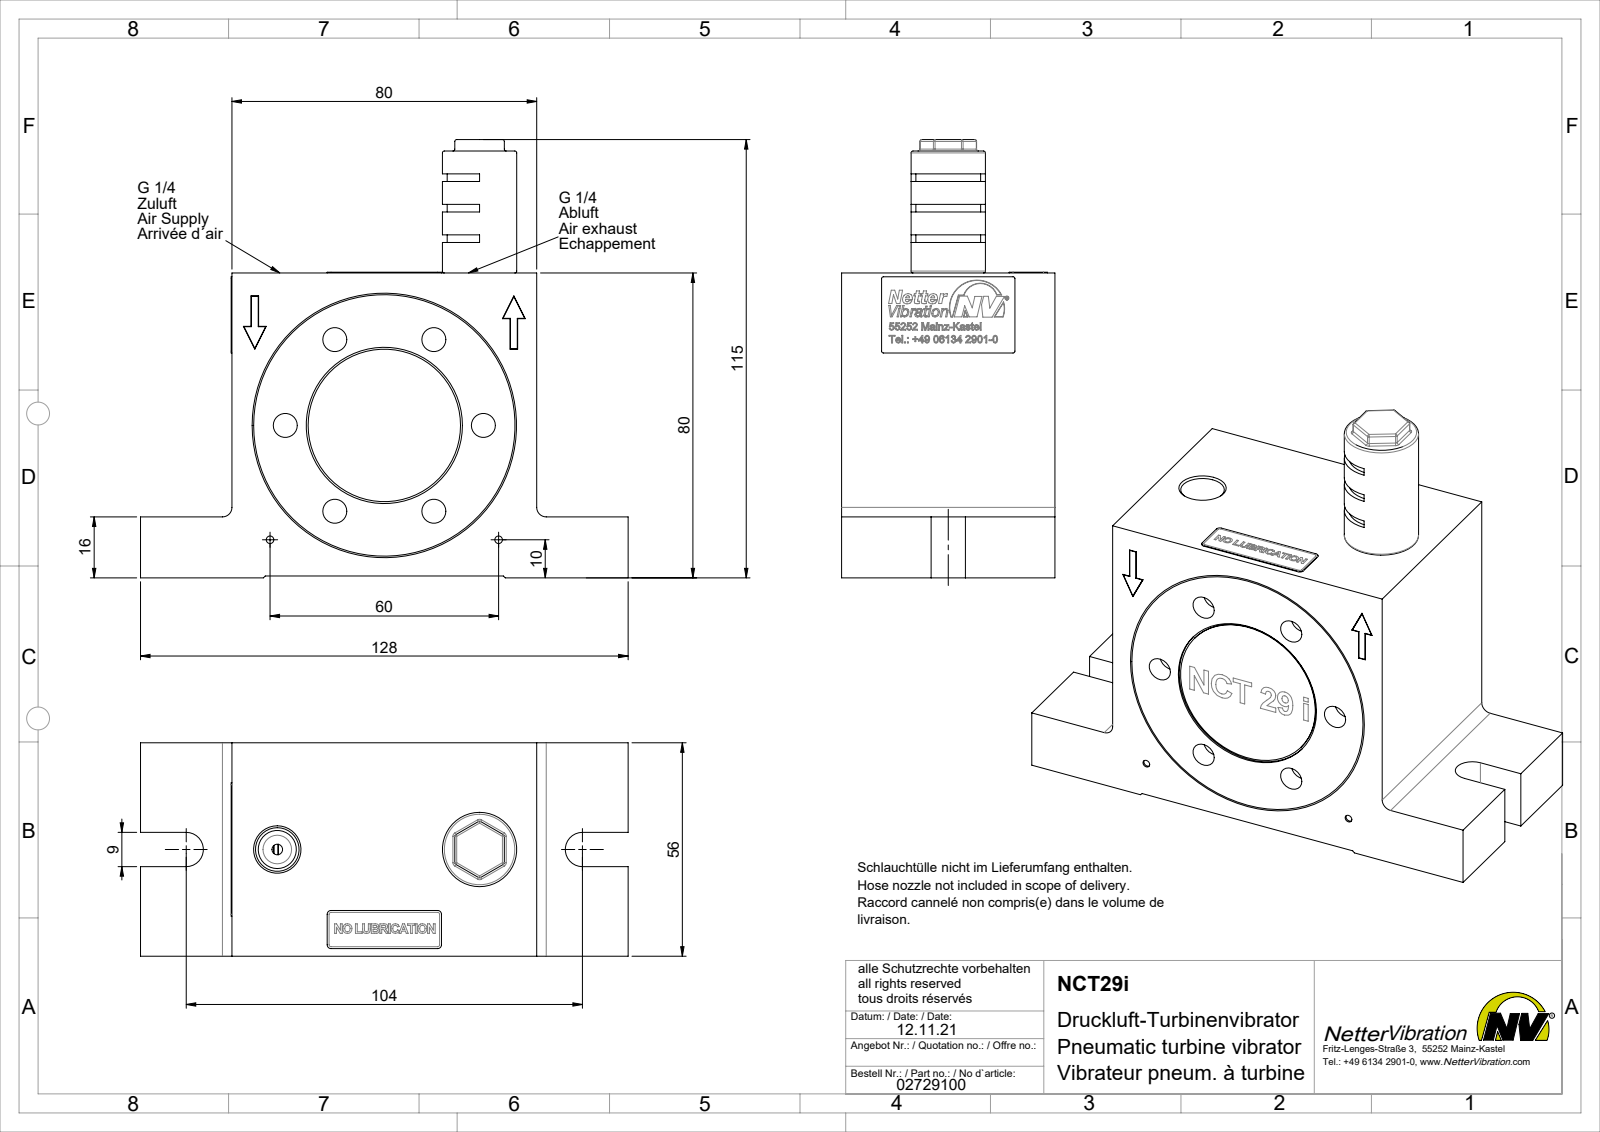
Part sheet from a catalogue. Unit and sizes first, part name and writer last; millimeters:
Units: millimetres
Overall size (bounding box): 128 × 115 × 56
Round holes (diameter × count): ⌀6.3 ×6, ⌀2 ×2, ⌀11.45 ×2, ⌀41 ×1, ⌀67.8 ×1
Round bosses / shafts (diameter × count): ⌀70 ×1, ⌀67.77 ×1, ⌀65.57 ×1, ⌀40 ×1, ⌀19.5 ×1, ⌀13.16 ×1
Partial cylindrical surfaces — rounded edges, fillets, slot ends (radius × count): R0.5 ×22, R1 ×4, R2.5 ×2, R4.5 ×2, R8.5 ×1
Main face-to-face distances: 80, 0.5, 56, 16, 8, 8.5, 48, 16.5, 39.5, 79.5
Hole centre spacings: 26, 45.03, 18.57, 30.27, 42.43, 43.65, 45.04, 52.01
Volume: 435 116 mm³ · Surface area: 60 474 mm²
Bodies: 6 solids, 338 faces (206 planar, 75 cylindrical, 57 other)
Part name (STEP PRODUCT): NCT 29i Turbinenvibrator #02729100
STEP written by: SolidWorks 2015 (AUTOMOTIVE_DESIGN)
